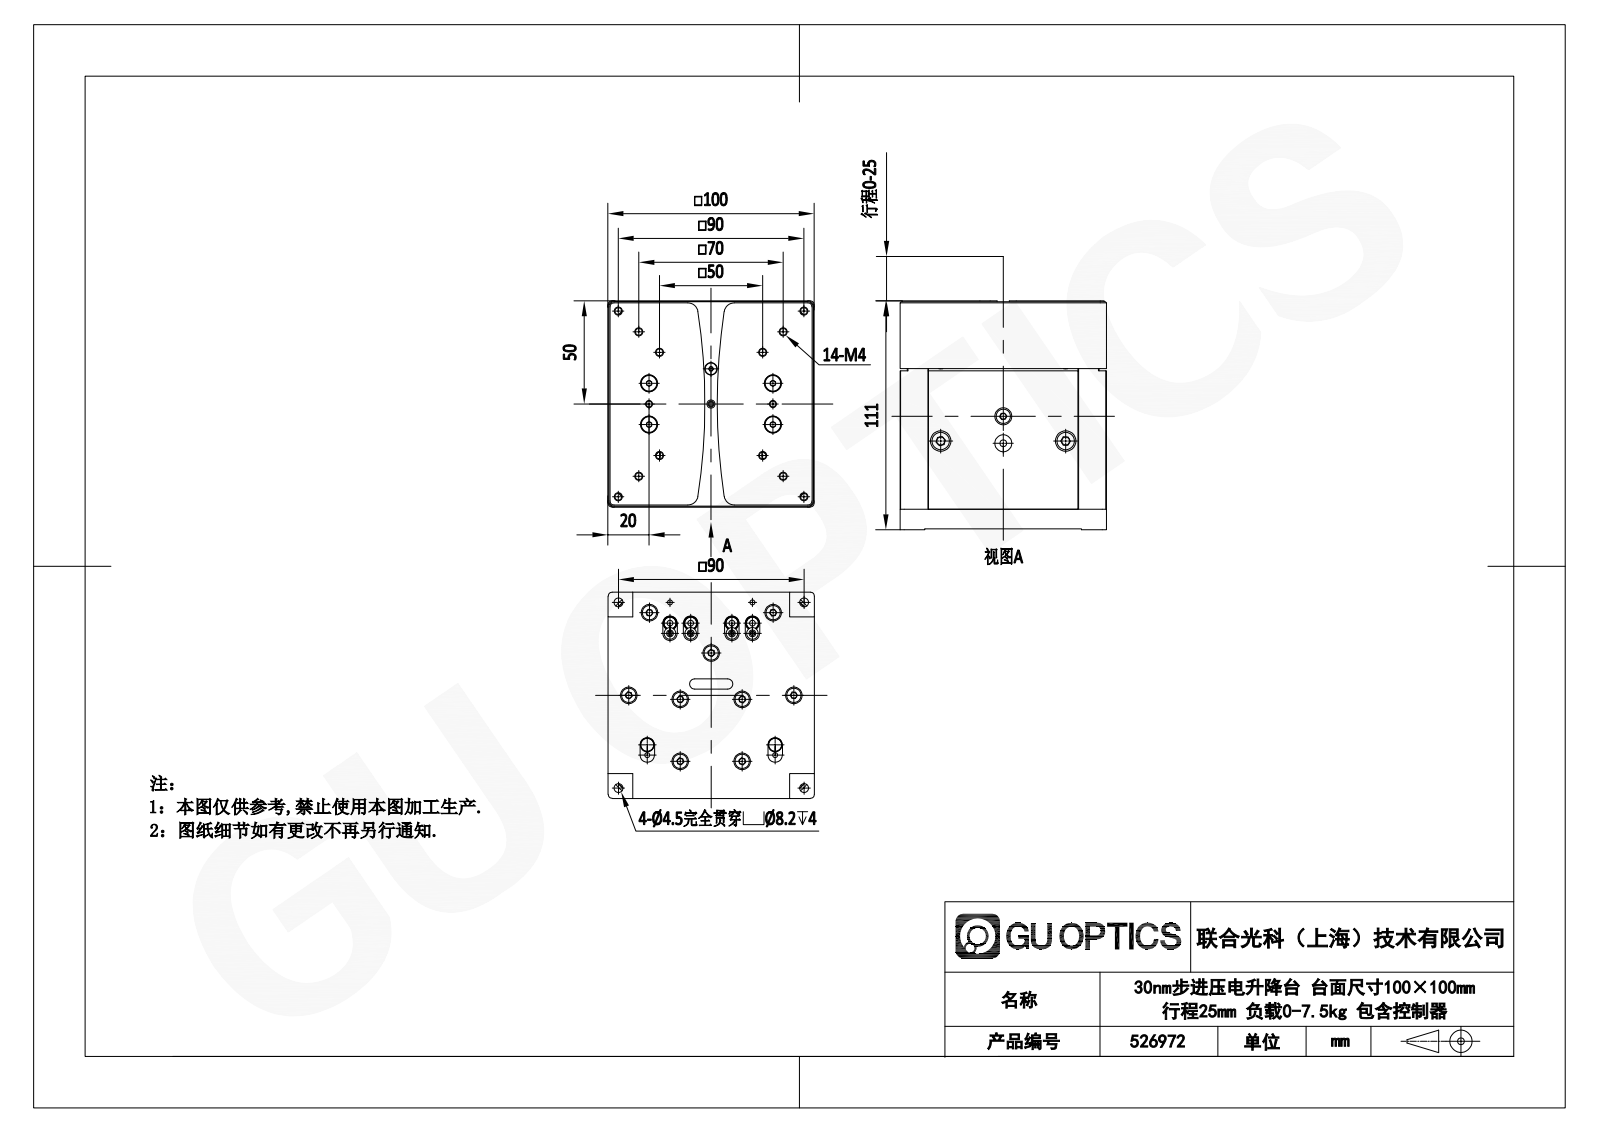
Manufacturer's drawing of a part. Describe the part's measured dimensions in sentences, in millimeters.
The part is named "hexagon socket head cap screws gb_GB_FASTENER_SCREWS_HSHCS M5X16-N; 526967; VR4_80HX7Z_0__AF0_ASM; hexagon socket button head screws gb_GB_SOCKET_TYPE7 M3X6-S (+7 more)". Its 3-D file was written by "SolidWorks 2020 (CONFIG_CONTROL_DESIGN)". It is 46 solids with 2325 faces: 929 planar, 696 cylindrical and 700 other. Overall it measures 111 by 100 by 100 millimeters. Its volume is 550 951 cubic millimeters and its surface area 200 867 square millimeters. Round holes: 24 of diameter 3.3, 23 of diameter 8, 20 of diameter 4.5, 15 of diameter 3, 11 of diameter 2.5, 8 of diameter 4.3, 8 of diameter 8.25, 7 of diameter 6.1, 6 of diameter 6.5, 4 of diameter 5.5, 4 of diameter 6.2, 4 of diameter 8.2. Round bosses or shafts: 25 of diameter 4, 14 of diameter 7, 10 of diameter 5, 8 of diameter 8.5, 5 of diameter 3, 4 of diameter 9.5, 4 of diameter 7.64, 4 of diameter 6. Partial cylindrical surfaces (rounded edges, fillets, slot ends): 18 of radius 1.5, 12 of radius 2, 12 of radius 3, 12 of radius 3.5, 9 of radius 1, 8 of radius 2.5, 8 of radius 5, 4 of radius 10. The main face-to-face distances are 100, 93.5, 0.5, 9.5, 110.5, 101, 41, 97, 59, 3. The hole center spacings are 40, 11.18, 30, 40.31, 90, 5, 10, 25.
